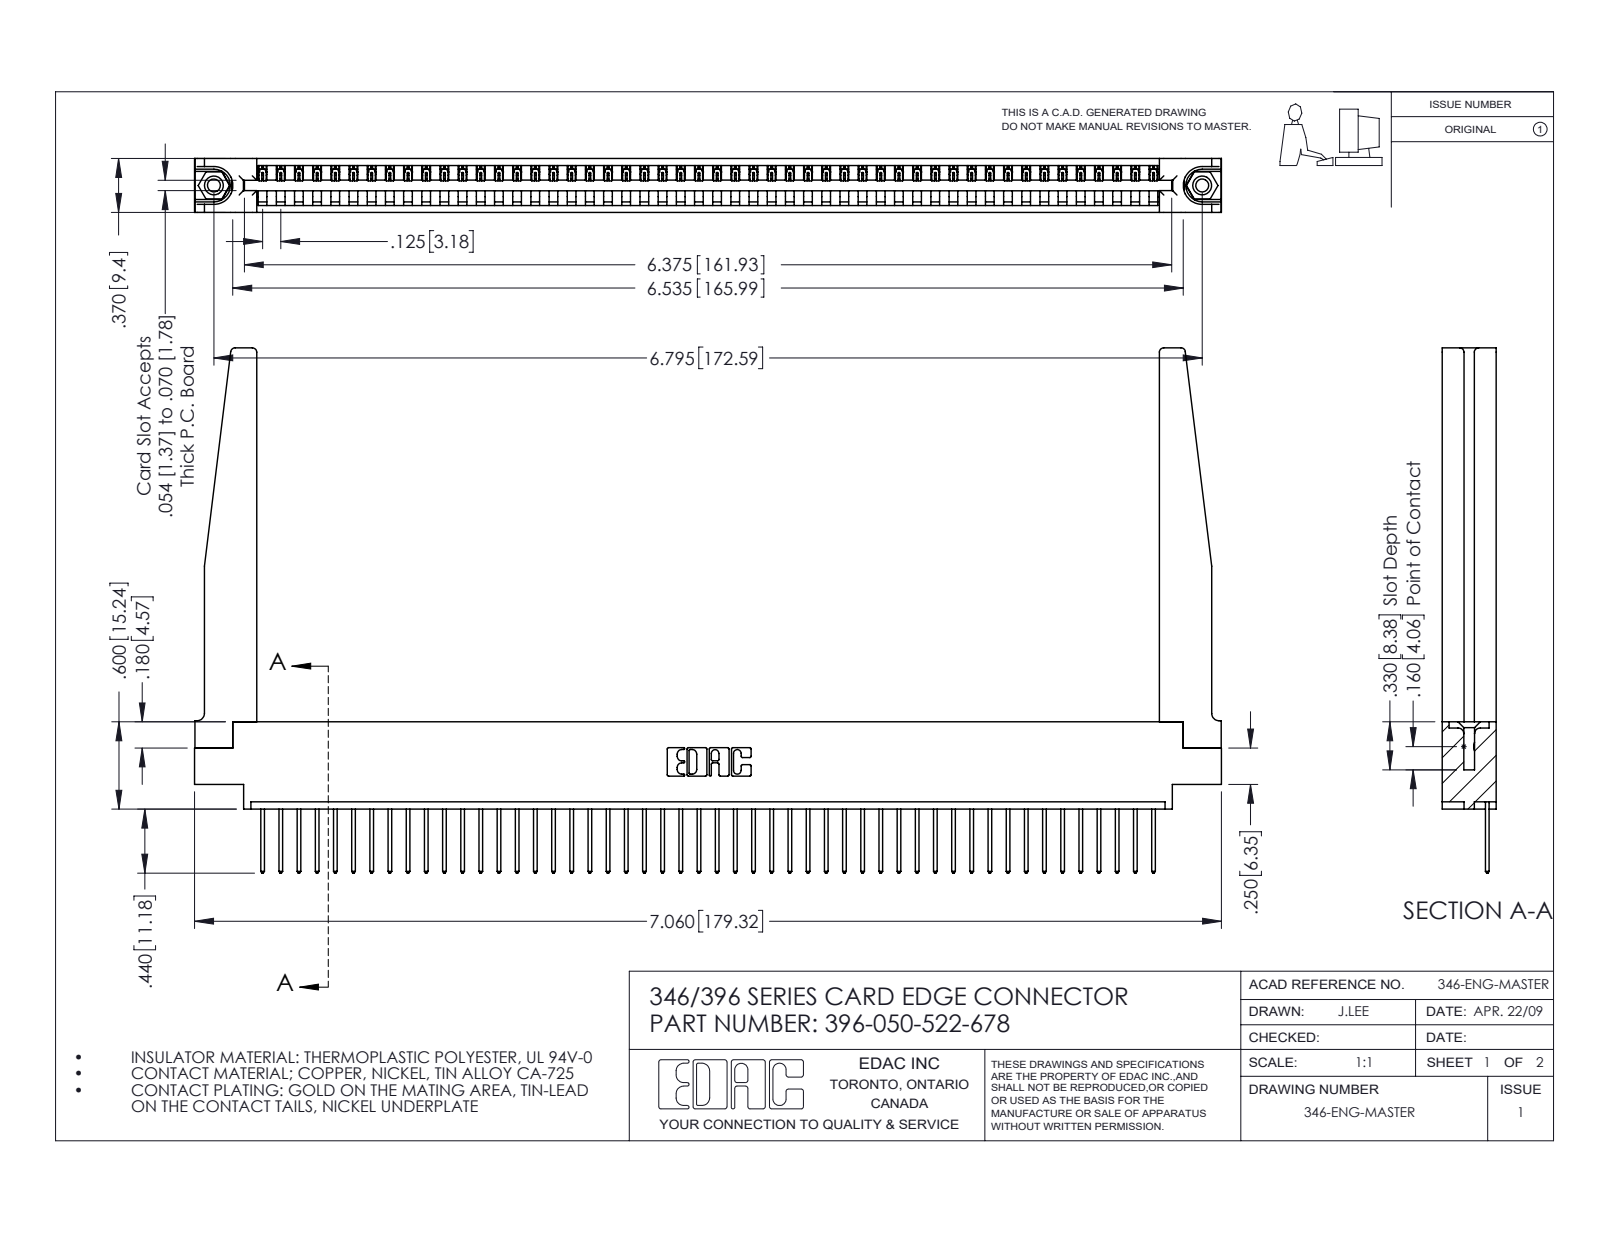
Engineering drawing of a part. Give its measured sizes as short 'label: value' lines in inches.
name: 396-050-522-678; 346-220-078_345-220-078; 346 Part_0.170 Offset - 0.156 Dia-TH; 345-250-001_345-250-001-102 (+1 more)
written by: SolidWorks 2016 (CONFIG_CONTROL_DESIGN)
unit: in
bodies: 55 solids, 3260 faces (2222 planar, 986 cylindrical, 52 other)
size: 7.06 × 3.61 × 0.37
volume: 1.463 in³; area: 43.88 in²
holes: 2× ⌀0.089, 2× ⌀0.125, 2× ⌀0.156, 1× ⌀0.064
bosses: 2× ⌀0.155
rounds: 100× R0.006, 100× R0.01, 22× R0.01, 8× R0.03, 6× R0.007, 6× R0.031, 3× R0.026, 2× R0.031
face distances: 0.37, 0.048, 0.322, 0.072, 0.25, 0.148, 0.15, 0.298, 0.025, 0.222
hole spacings: 0.246, 6.586, 6.795
